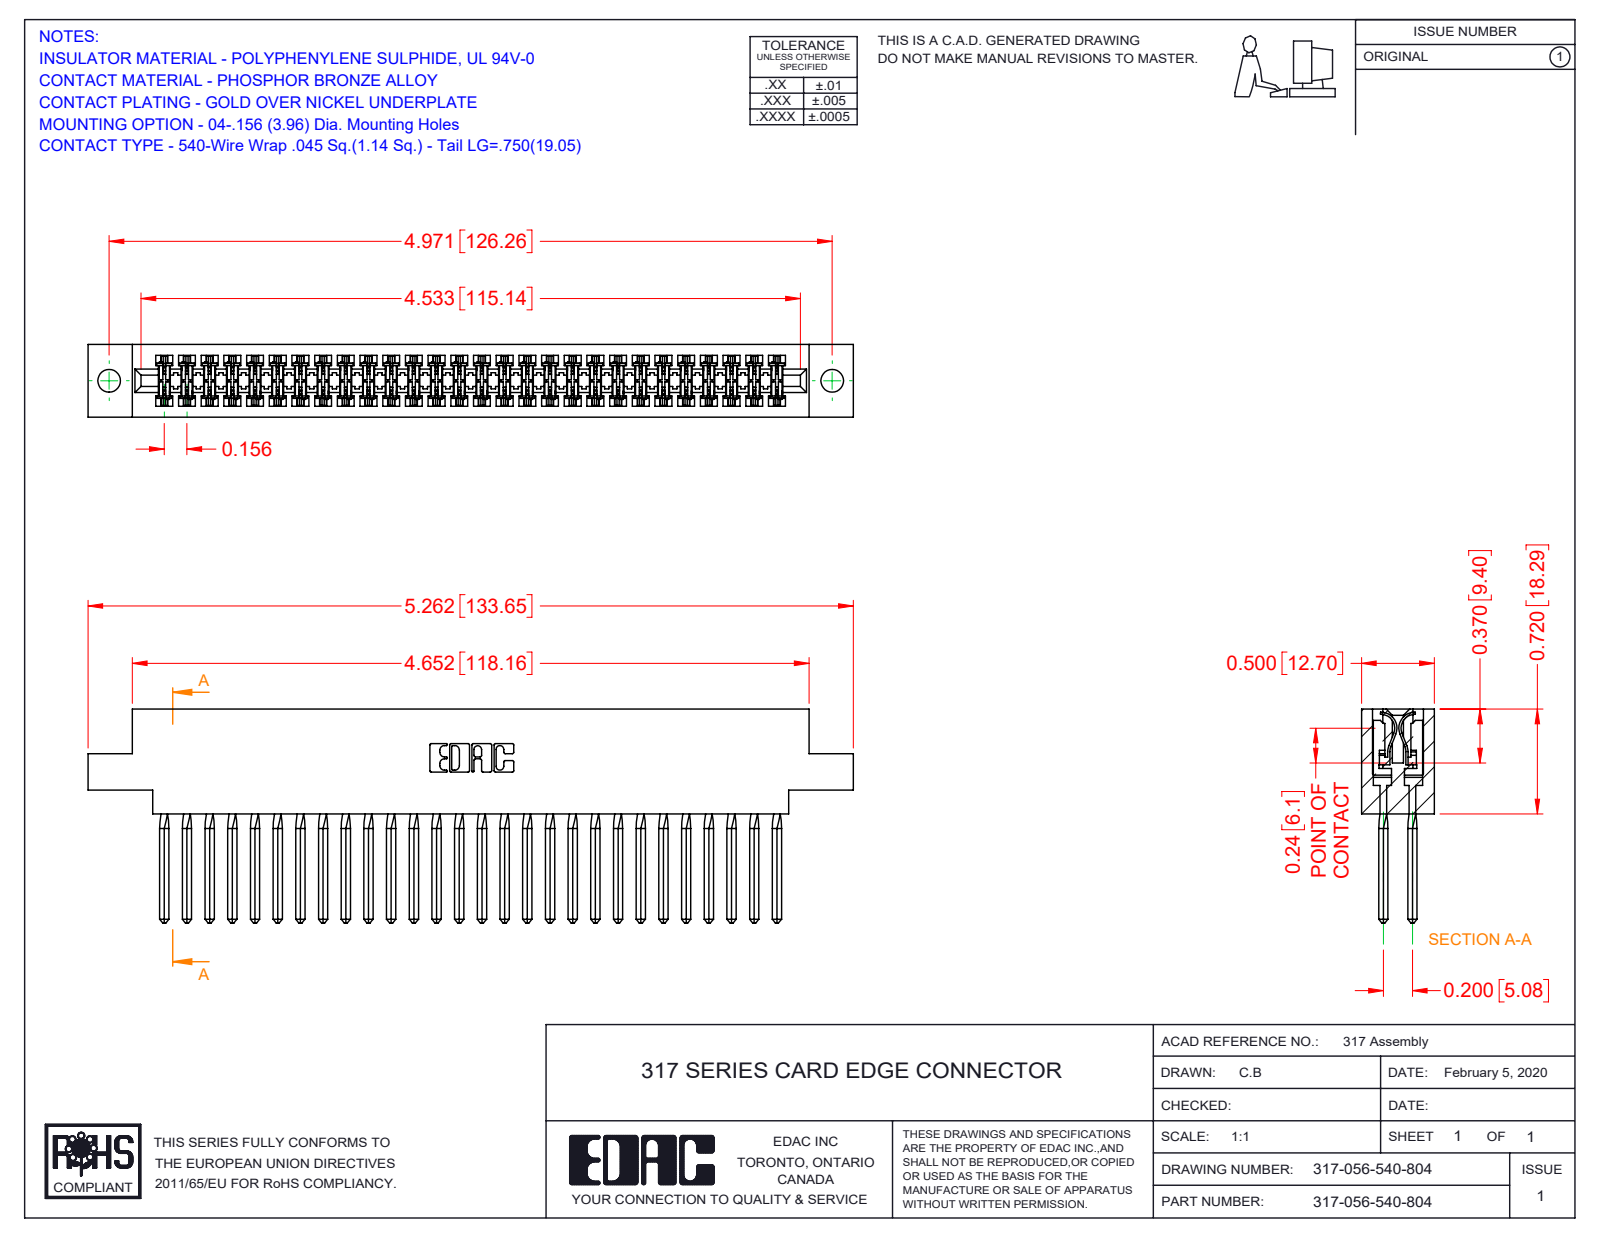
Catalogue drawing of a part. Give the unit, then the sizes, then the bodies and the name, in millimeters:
Units: millimetres
Overall size (bounding box): 133.7 × 37.3 × 12.7
Round holes (diameter × count): ⌀4 ×2
Partial cylindrical surfaces — rounded edges, fillets, slot ends (radius × count): R0.4 ×112, R0.3 ×22, R0.2 ×6, R0.8 ×6, R0.7 ×3, R2.4 ×2, R2.5 ×2, R2.8 ×2
Main face-to-face distances: 12.7, 1.9, 10.8, 8.9, 2.8, 5, 2.4, 5.1, 18.3, 2.9
Hole centre spacings: 126.3
Volume: 21 880 mm³ · Surface area: 31 900 mm²
Bodies: 57 solids, 5086 faces (4146 planar, 716 cylindrical, 224 other)
Part name (STEP PRODUCT): 317 Part_.156 Dia - TH; 317-290-001_540; 317-056-540-804
STEP written by: SolidWorks 2016 (CONFIG_CONTROL_DESIGN)
